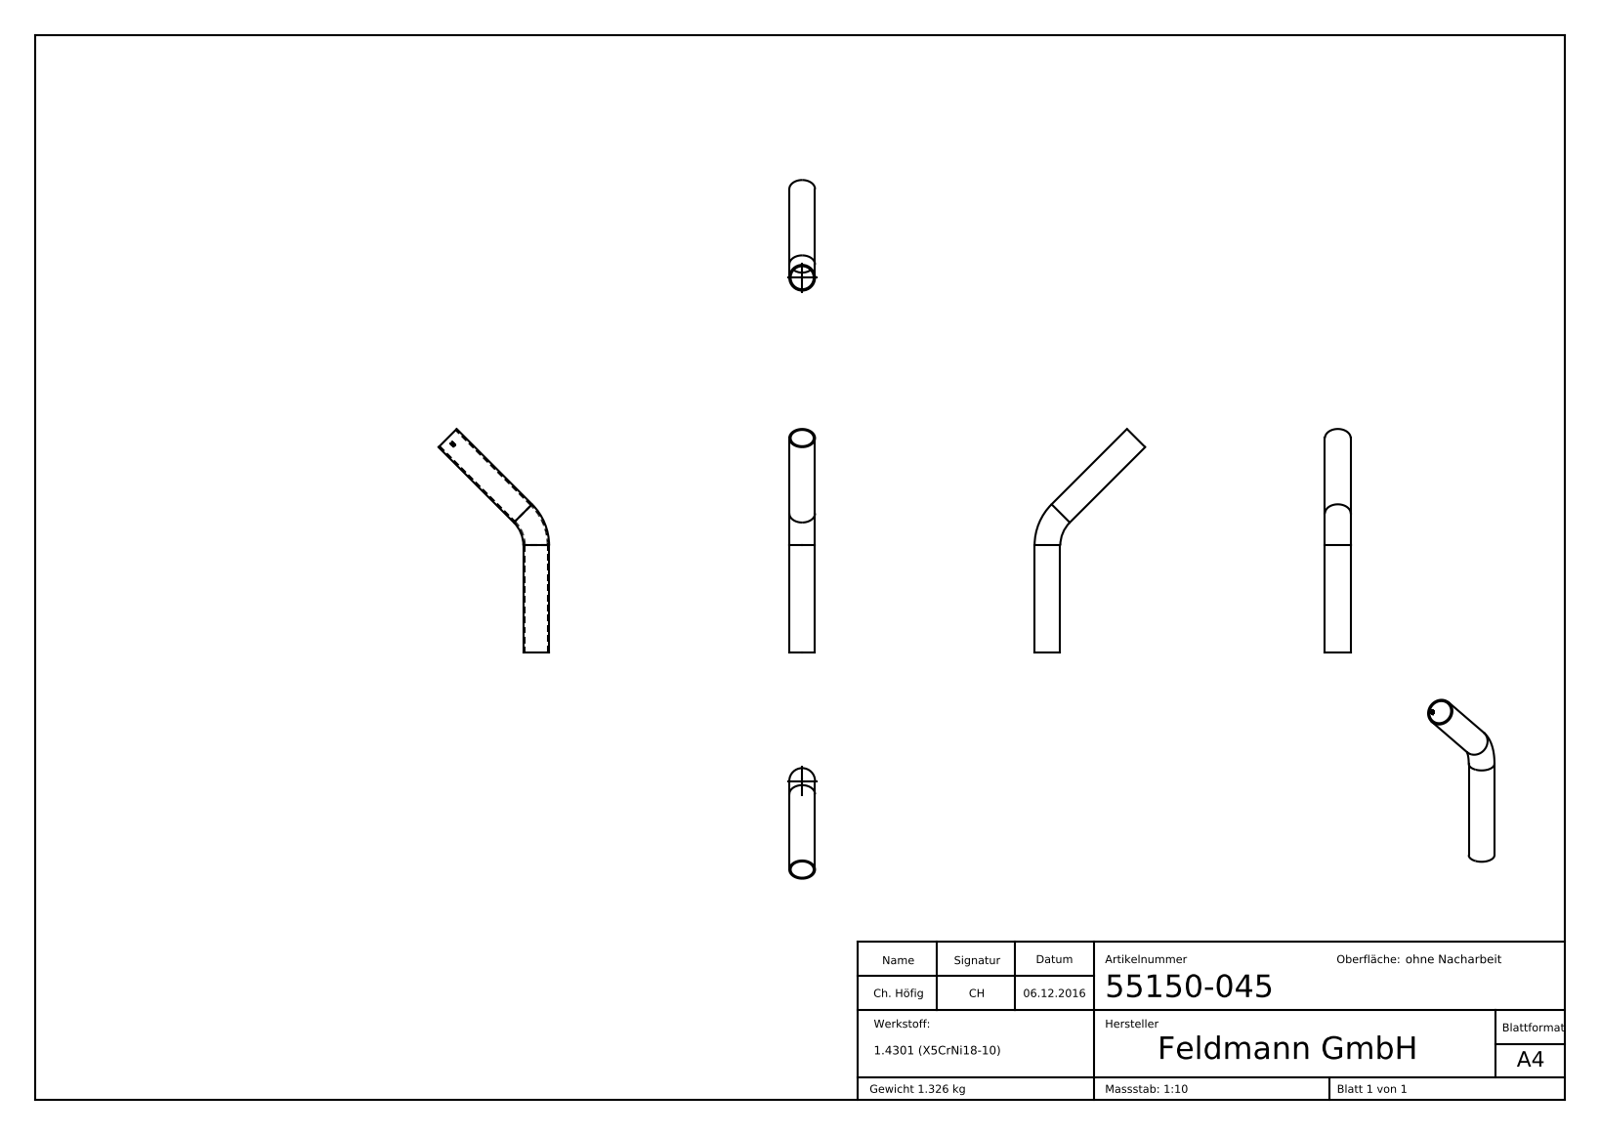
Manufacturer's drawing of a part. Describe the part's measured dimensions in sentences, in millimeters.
The part is named "55150-045". Its 3-D file was written by "SolidWorks 2015 (CONFIG_CONTROL_DESIGN)". It is 1 solid with 236 faces: 103 planar, 31 cylindrical and 102 other. Overall it measures 418.6 by 207.54 by 48.3 millimeters. Its volume is 167 898 cubic millimeters and its surface area 135 048 square millimeters. Round holes: 2 of diameter 43.3. Round bosses or shafts: 2 of diameter 48.3. Partial cylindrical surfaces (rounded edges, fillets, slot ends): 1 of radius 21.75. The main face-to-face distances are 0.39, 2.96, 2.03, 4.89, 2.42, 5.28, 3.8, 0.67, 7.31, 2.55.
